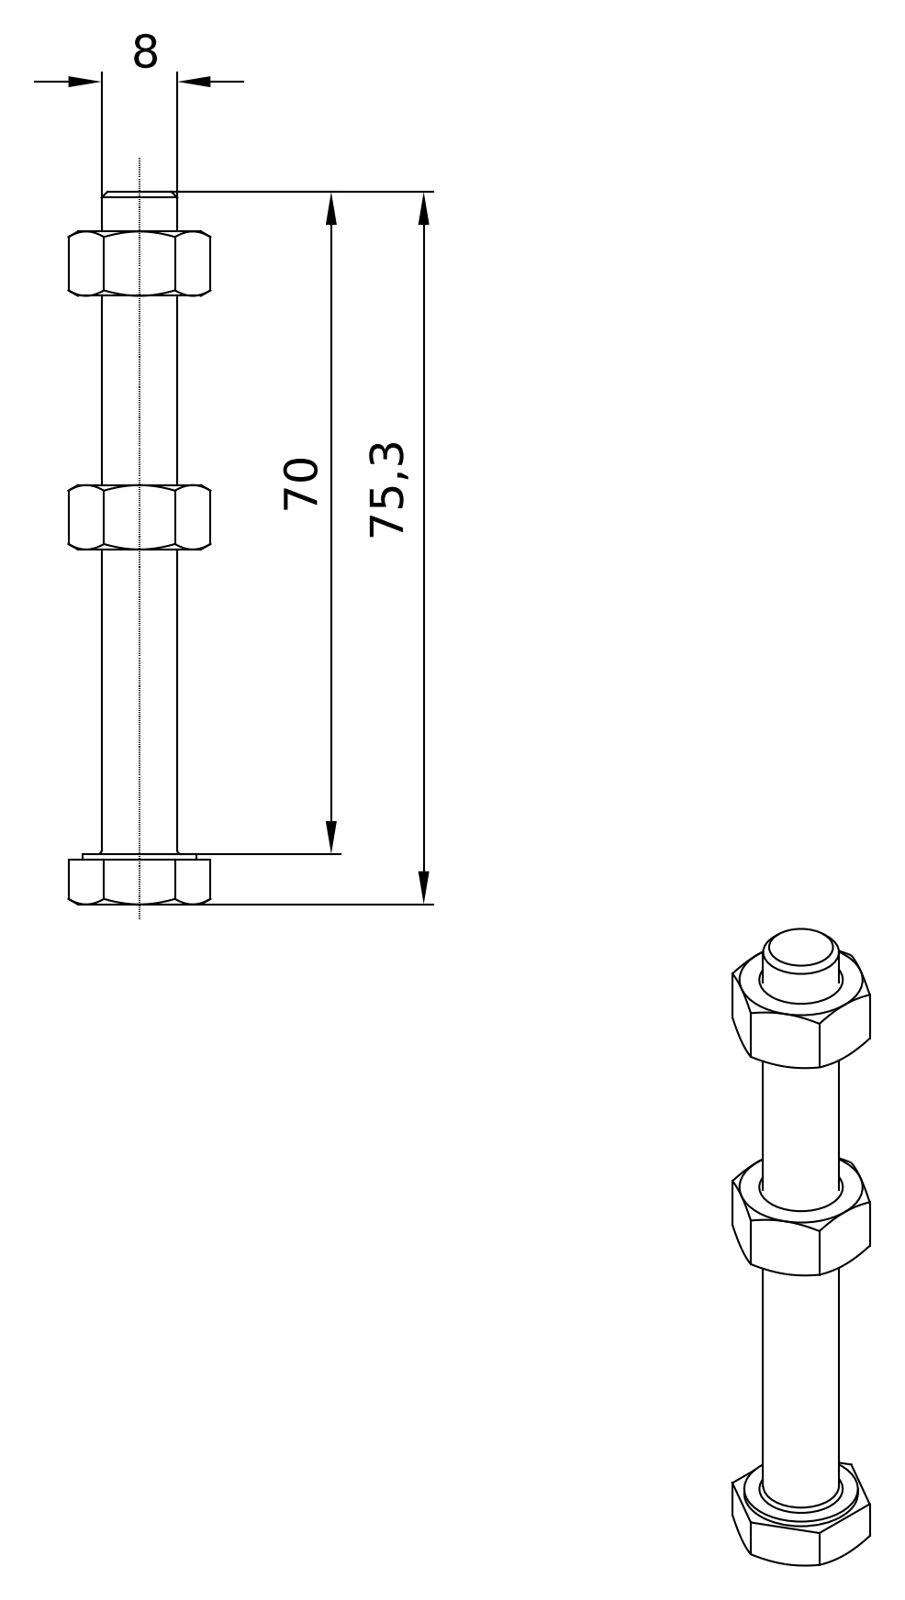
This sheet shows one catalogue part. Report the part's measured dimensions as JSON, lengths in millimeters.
{"part_name": "800 047", "step_written_by": "Autodesk Inventor 2024 (AUTOMOTIVE_DESIGN)", "units": "millimeters", "bodies": {"solids": 3, "faces": 47, "planar": 26, "cylindrical": 5, "other": 16}, "overall_size": [75.3, 15.01, 13], "volume_mm3": 5602, "surface_area_mm2": 3454, "round_holes": [[6.65, 1]], "round_bosses_or_shafts": [[11.4, 1], [8, 1], [7.32, 1]], "face_to_face_distances": [13, 35.12, 6.5, 5.3, 16.49, 51.61, 11.19, 46.31, 22.99, 58.11]}
